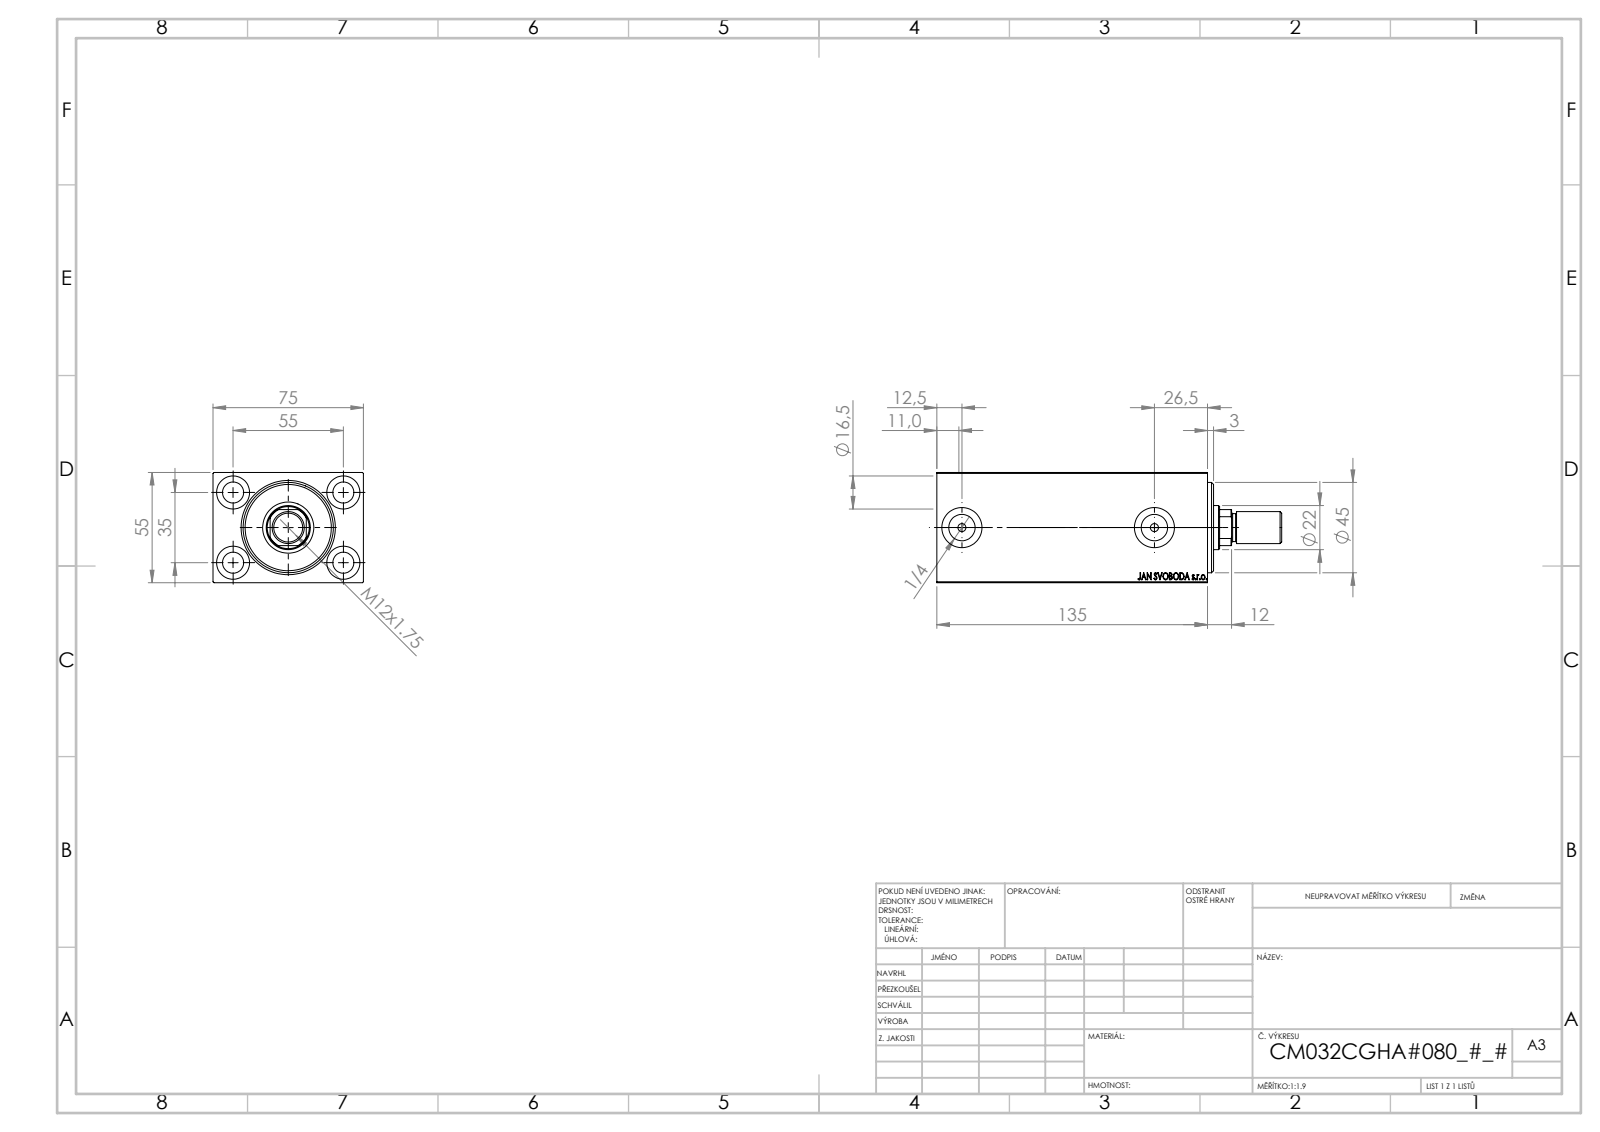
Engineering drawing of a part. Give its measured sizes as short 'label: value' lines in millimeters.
name: V450CM_C_VCP; V450CM_C_Body; V450CM_MALE_METRIC; V450CM_VC_B
written by: SolidWorks 2019 (CONFIG_CONTROL_DESIGN)
unit: mm
bodies: 4 solids, 875 faces (411 planar, 64 cylindrical, 400 other)
size: 172 × 75 × 55
volume: 471 831 mm³; area: 97 533 mm²
holes: 5× ⌀10.5, 4× ⌀16.5, 2× ⌀4, 2× ⌀13.16, 2× ⌀20, 1× ⌀22, 1× ⌀25.5, 1× ⌀32, 1× ⌀34, 1× ⌀45
bosses: 1× ⌀16, 1× ⌀14
rounds: 1× R10.5
face distances: 55, 75, 10, 125, 135, 130, 5, 120, 11, 124
hole spacings: 32.6, 35, 55, 65.19, 96
